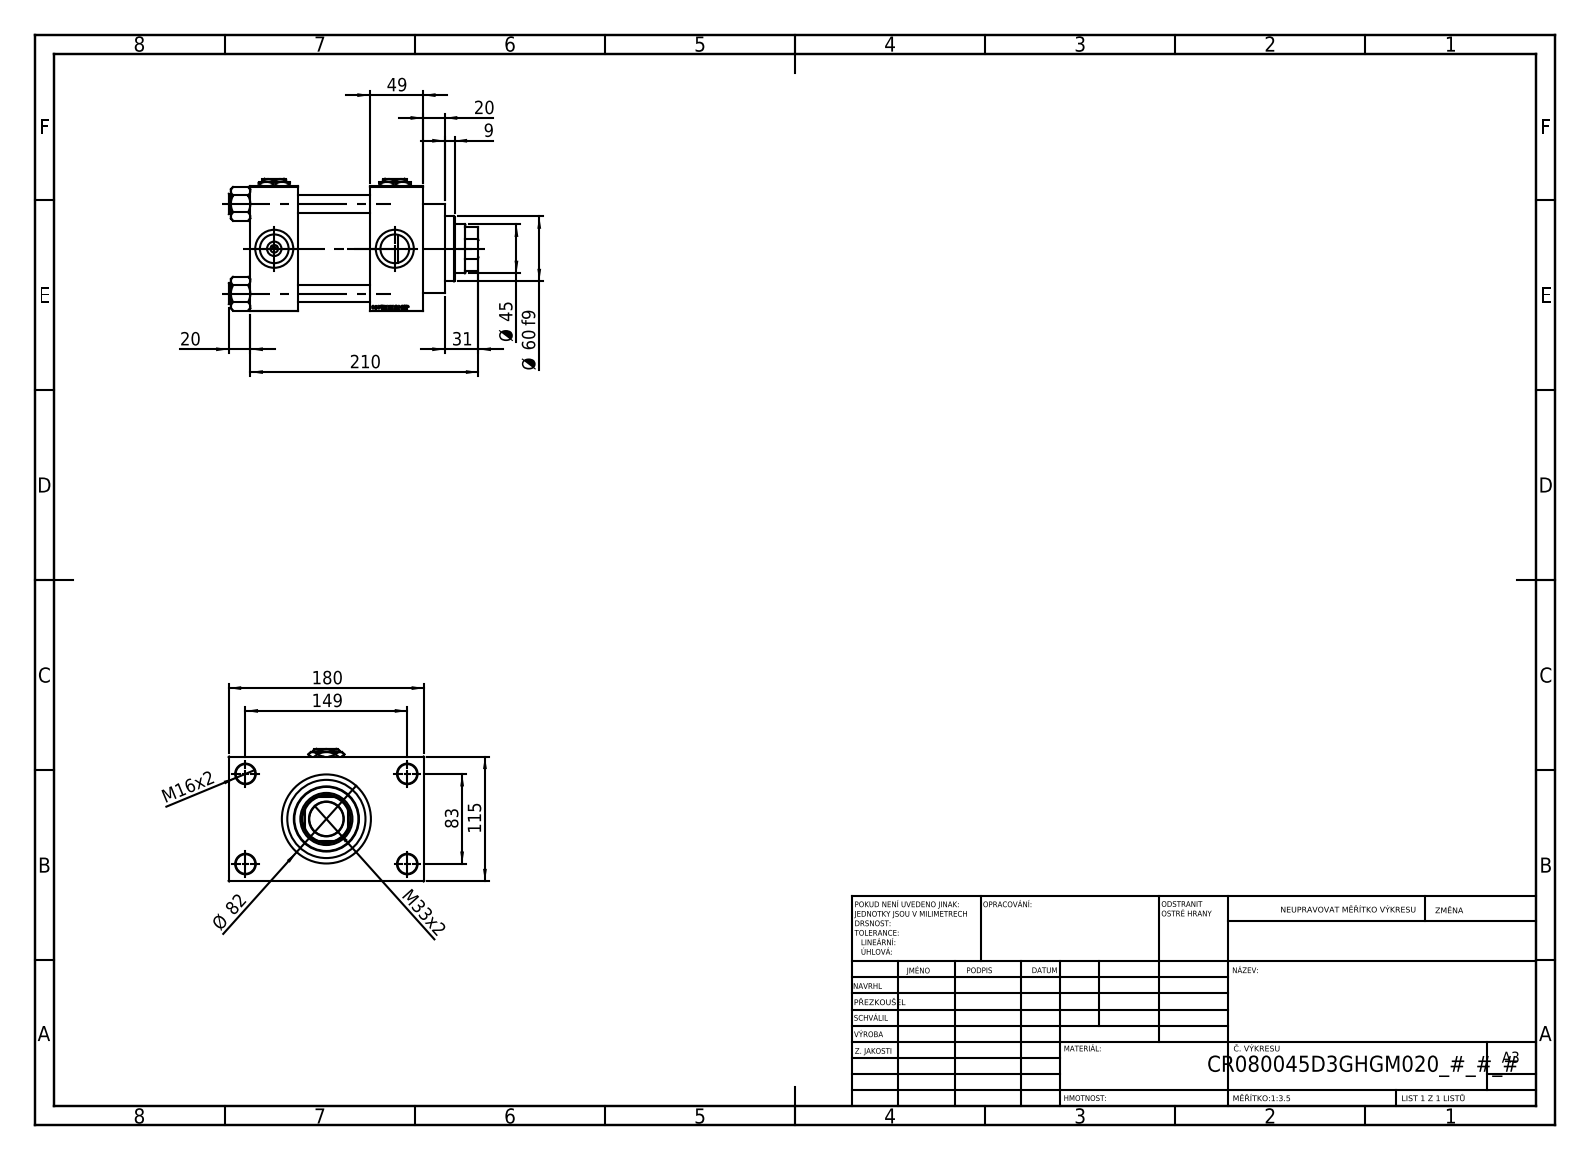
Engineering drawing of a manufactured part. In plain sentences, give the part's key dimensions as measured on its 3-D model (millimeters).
The part is named "V215CR_D_TYCINKA; V215CR_VCP_D; V215_VC_A; V215CR_D_Body (+2 more)". Its 3-D file was written by "SolidWorks 2019 (CONFIG_CONTROL_DESIGN)". It is 13 solids with 1252 faces: 593 planar, 99 cylindrical and 560 other. Overall it measures 230 by 180 by 122 millimeters. Its volume is 1 990 000 cubic millimeters and its surface area 309 159 square millimeters. Round holes: 4 of diameter 16, 4 of diameter 18, 4 of diameter 26.44, 4 of diameter 35, 3 of diameter 7, 1 of diameter 31.5, 1 of diameter 45, 1 of diameter 48, 1 of diameter 61, 1 of diameter 72, 1 of diameter 80. Round bosses or shafts: 4 of diameter 19, 1 of diameter 86, 1 of diameter 82, 1 of diameter 60. Partial cylindrical surfaces (rounded edges, fillets, slot ends): 1 of radius 22. The main face-to-face distances are 115, 110, 66, 49, 44, 159, 32.5, 147.5, 20, 69. The hole center spacings are 33.15, 58.48, 82.7, 85.28, 89.24, 115.85, 142.43, 83.
